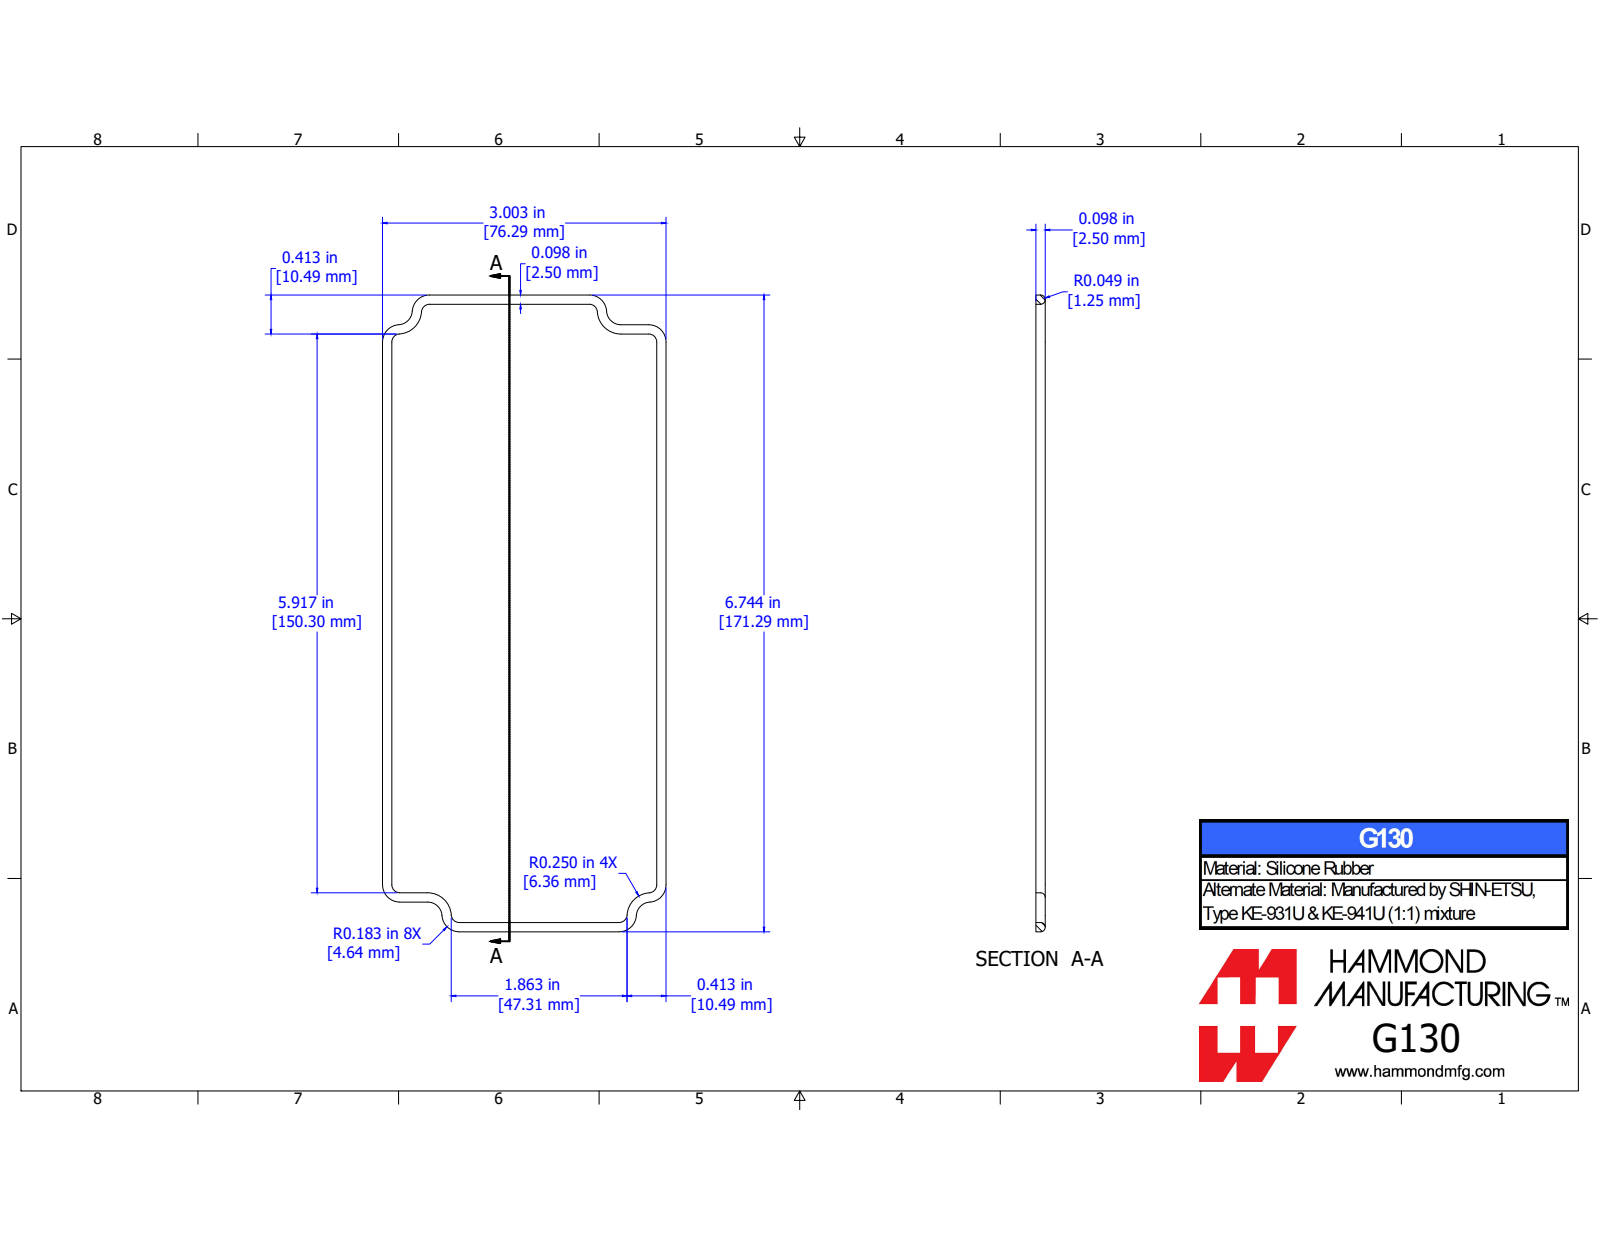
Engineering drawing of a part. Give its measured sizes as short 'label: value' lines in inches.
name: 1590Z130G
written by: SolidWorks 2019 (CONFIG_CONTROL_DESIGN)
unit: in
bodies: 1 solid, 74 faces (14 planar, 12 cylindrical, 48 other)
size: 6.719 × 2.978 × 0.108
volume: 0.158 in³; area: 6.557 in²
rounds: 12× R0.03
face distances: 2.894, 0.108, 6.634, 0.315, 6.319, 6.004
